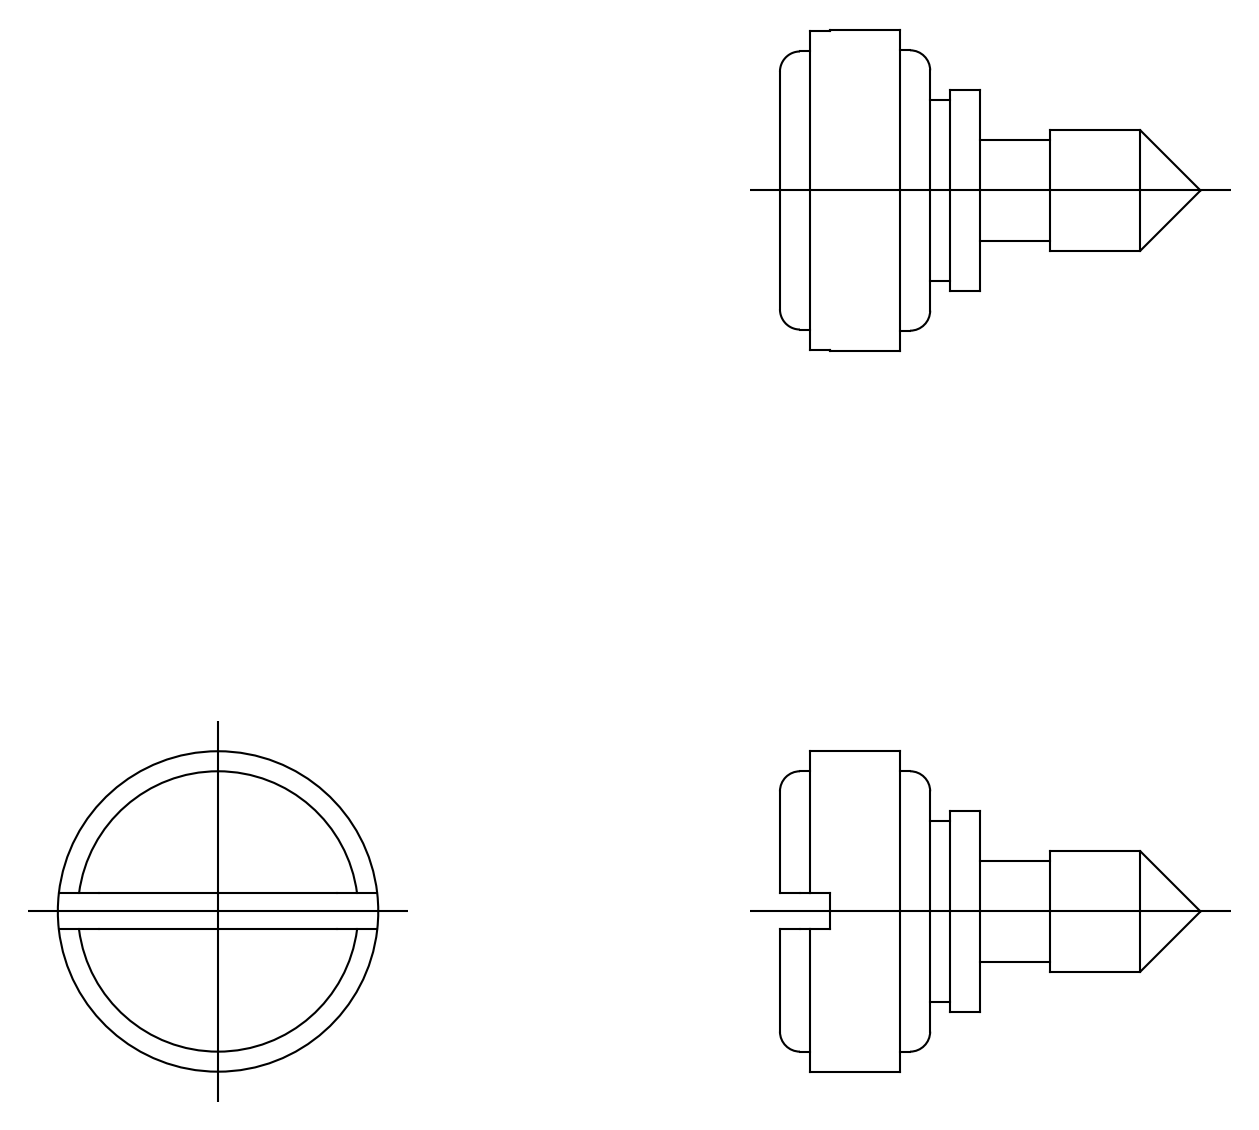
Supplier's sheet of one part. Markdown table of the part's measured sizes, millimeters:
| quantity | value |
| --- | --- |
| STEP written by | spGate 19.8.4 (****-****-****-****) (AUTOMOTIVE_DESIGN) |
| units | millimeters |
| bodies | 1 solid, 32 faces (12 planar, 14 cylindrical, 6 other) |
| overall size | 21 × 16 × 16 |
| volume | 1 689 mm³ |
| surface area | 1 060 mm² |
| round bosses / shafts (diameter × count) | 16 × 1, 14 × 1, 10 × 1, 9 × 1, 6 × 1, 5 × 1 |
| main face-to-face distances | 1.5, 6, 2.5, 10, 8.5, 7.5, 4, 4.5, 1.8, 2.48 |
